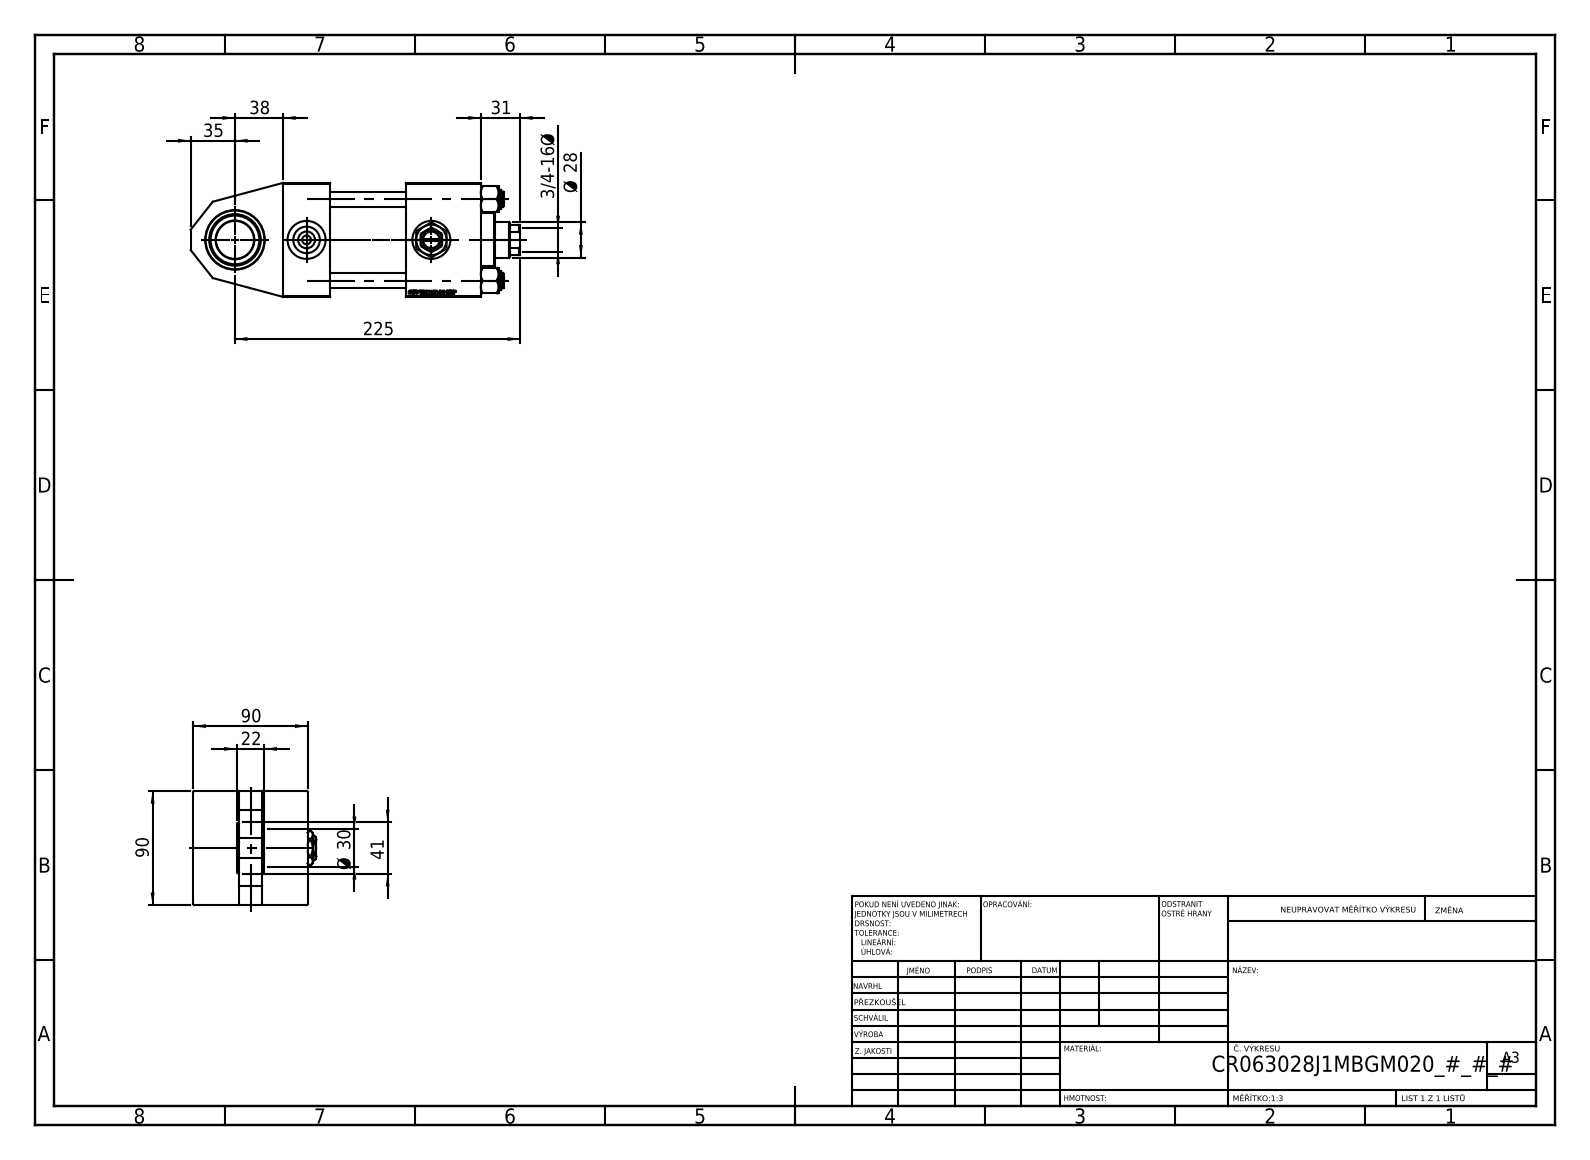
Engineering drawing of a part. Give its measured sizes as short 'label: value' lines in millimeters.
name: Zatka_pro_OIL_PORT; V215CR_J_Body; V215CR_J_VNITRNI_KROUZEK; V215CR_VCP_J (+3 more)
written by: SolidWorks 2019 (CONFIG_CONTROL_DESIGN)
unit: mm
bodies: 13 solids, 1193 faces (540 planar, 93 cylindrical, 560 other)
size: 260 × 97 × 90
volume: 1 029 000 mm³; area: 202 670 mm²
holes: 4× ⌀12, 3× ⌀30, 2× ⌀2.5, 2× ⌀7, 2× ⌀20.96, 1× ⌀18.5, 1× ⌀28, 1× ⌀31, 1× ⌀47, 1× ⌀50, 1× ⌀60, 1× ⌀63
bosses: 4× ⌀15, 1× ⌀69, 1× ⌀42
rounds: 1× R13.5
face distances: 90, 54, 36, 119, 37, 156, 97, 60, 59, 18
hole spacings: 32.39, 45.47, 64.3, 68.42, 28.25, 56.5, 90.93, 98.5
